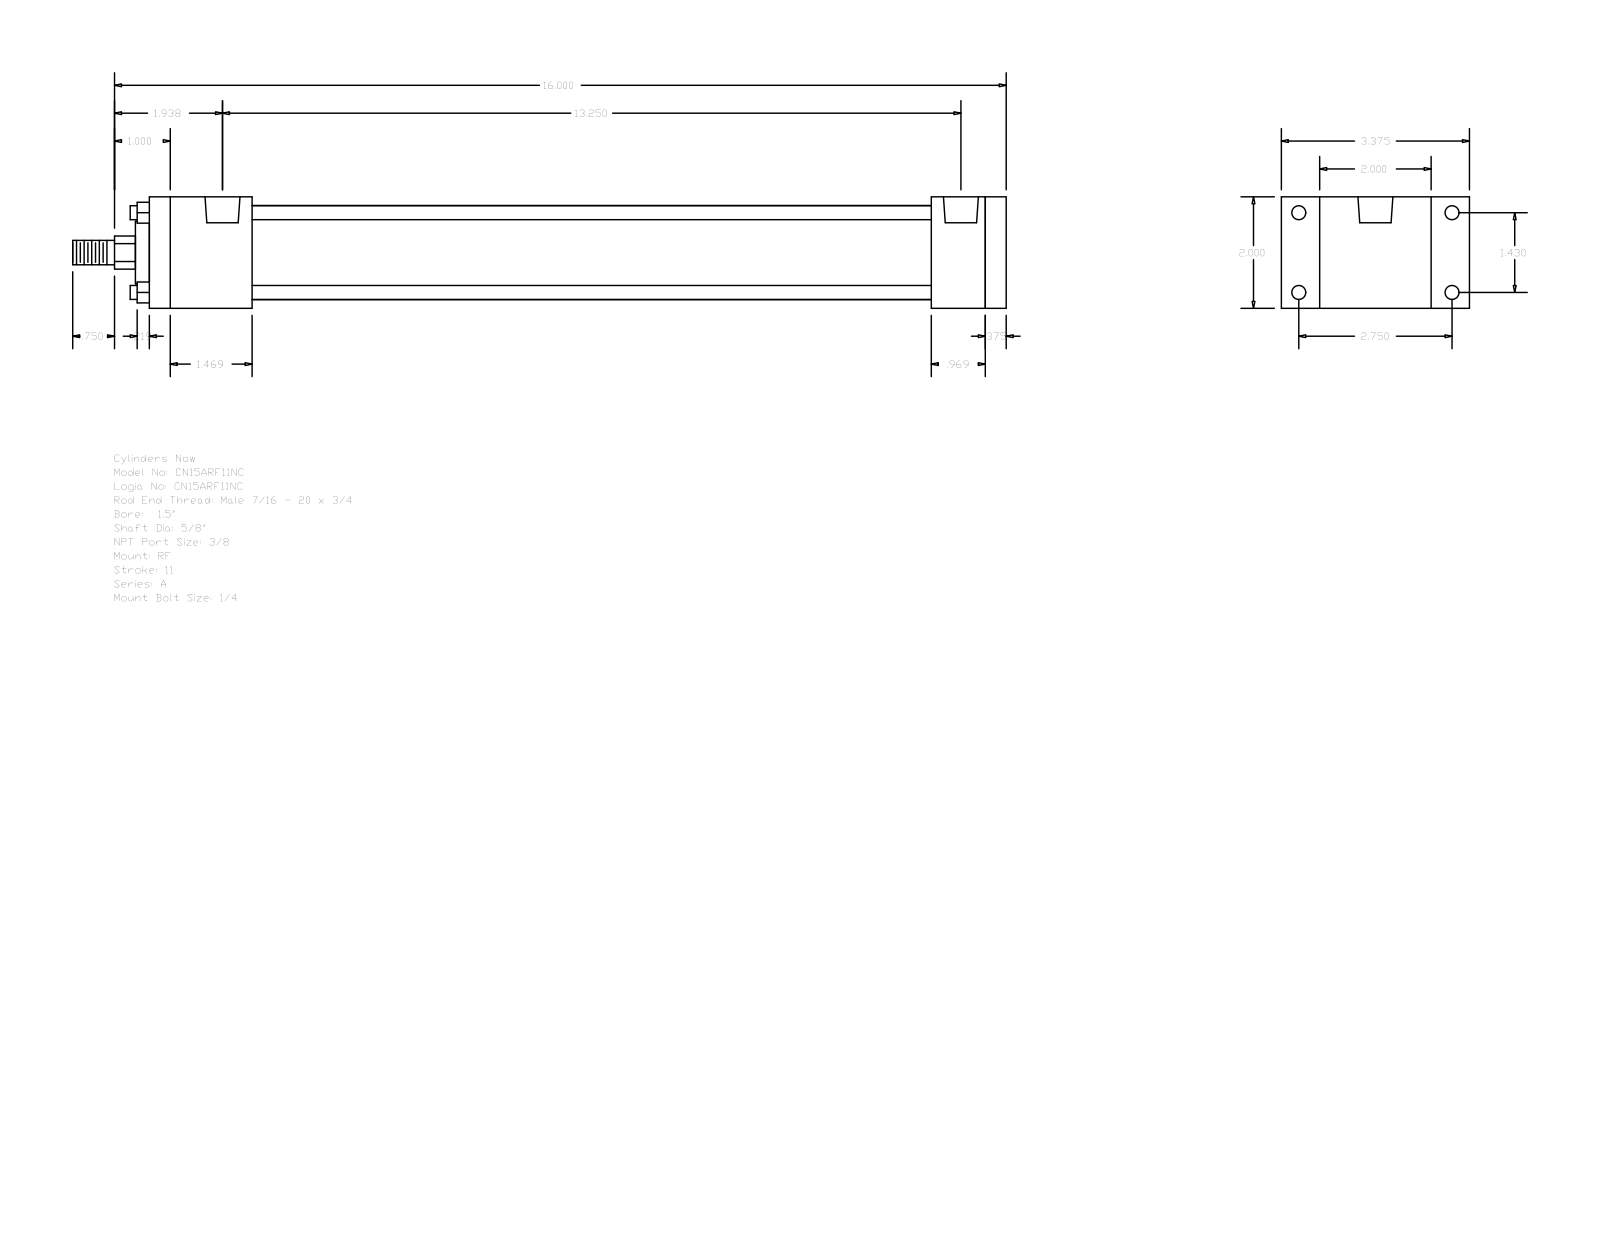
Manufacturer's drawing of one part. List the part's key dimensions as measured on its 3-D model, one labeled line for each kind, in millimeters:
Part name (STEP PRODUCT): A_RF__0150_0.625
STEP written by: GSSL Pune (CONFIG_CONTROL_DESIGN)
Units: millimetres
Bodies: 0 solids, 92 faces (64 planar, 28 cylindrical, 0 other)
Overall size (bounding box): 425.45 × 85.72 × 50.8
Round holes (diameter × count): ⌀5.56 ×4, ⌀6.35 ×4, ⌀15.93 ×2
Round bosses / shafts (diameter × count): ⌀6.35 ×4, ⌀42.93 ×1, ⌀28.57 ×1, ⌀15.88 ×1, ⌀11.11 ×1
Partial cylindrical surfaces — rounded edges, fillets, slot ends (radius × count): R7.54 ×1
Main face-to-face distances: 50.8, 9.52, 381, 390.52, 356.39, 24.61, 34.13, 46.83, 309.56, 334.17
Hole centre spacings: 3.97, 36.32, 69.84, 78.72, 328.61, 332.58, 336.55
